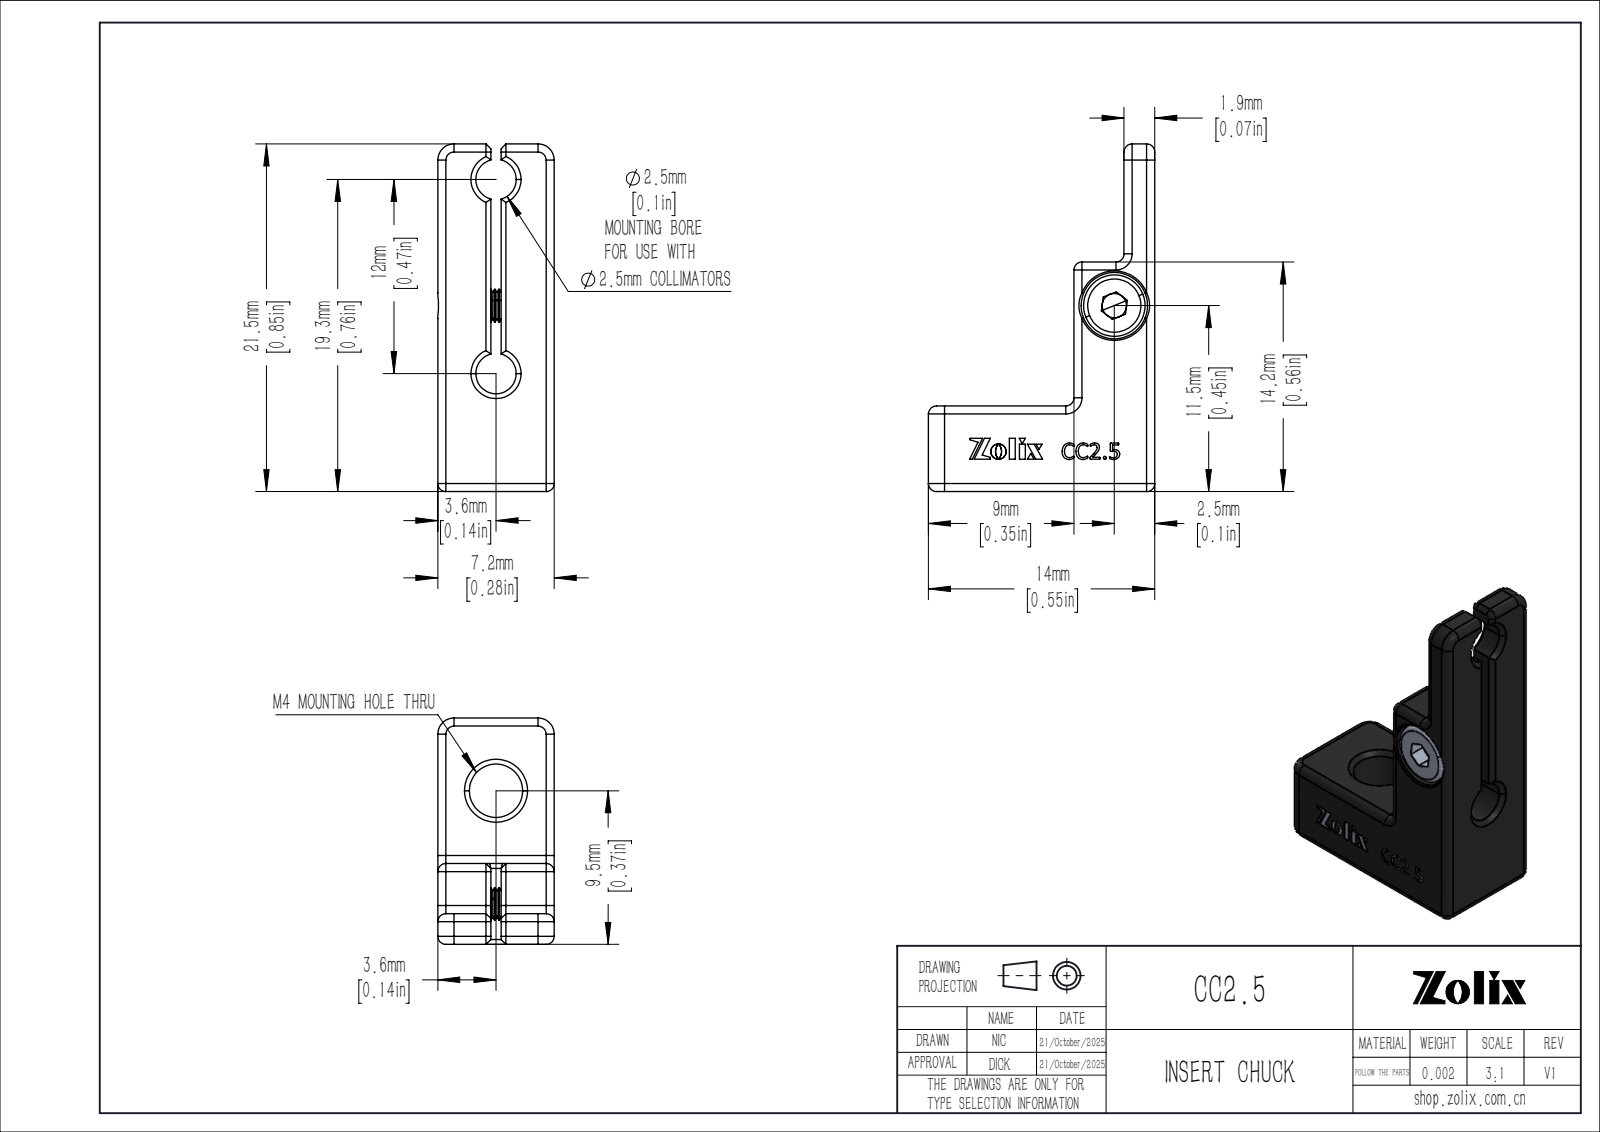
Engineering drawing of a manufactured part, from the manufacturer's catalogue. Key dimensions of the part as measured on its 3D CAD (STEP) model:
Part name (STEP PRODUCT): CC2.5
STEP written by: SolidWorks 2020 (CONFIG_CONTROL_DESIGN)
Units: millimetres
Bodies: 2 solids, 472 faces (235 planar, 74 cylindrical, 163 other)
Overall size (bounding box): 21.5 × 14 × 7.2
Volume: 827 mm³ · Surface area: 968 mm²
Round holes (diameter × count): ⌀2.5 ×2, ⌀1.6 ×1, ⌀2.4 ×1, ⌀3.3 ×1, ⌀4.1 ×1
Round bosses / shafts (diameter × count): ⌀3.8 ×1, ⌀2 ×1
Partial cylindrical surfaces — rounded edges, fillets, slot ends (radius × count): R0.5 ×20, R1 ×4
Main face-to-face distances: 7.2, 5.3, 5, 3.28, 3.92, 3.1, 1.9, 3.29, 3.91, 0.63
Hole centre spacings: 12
